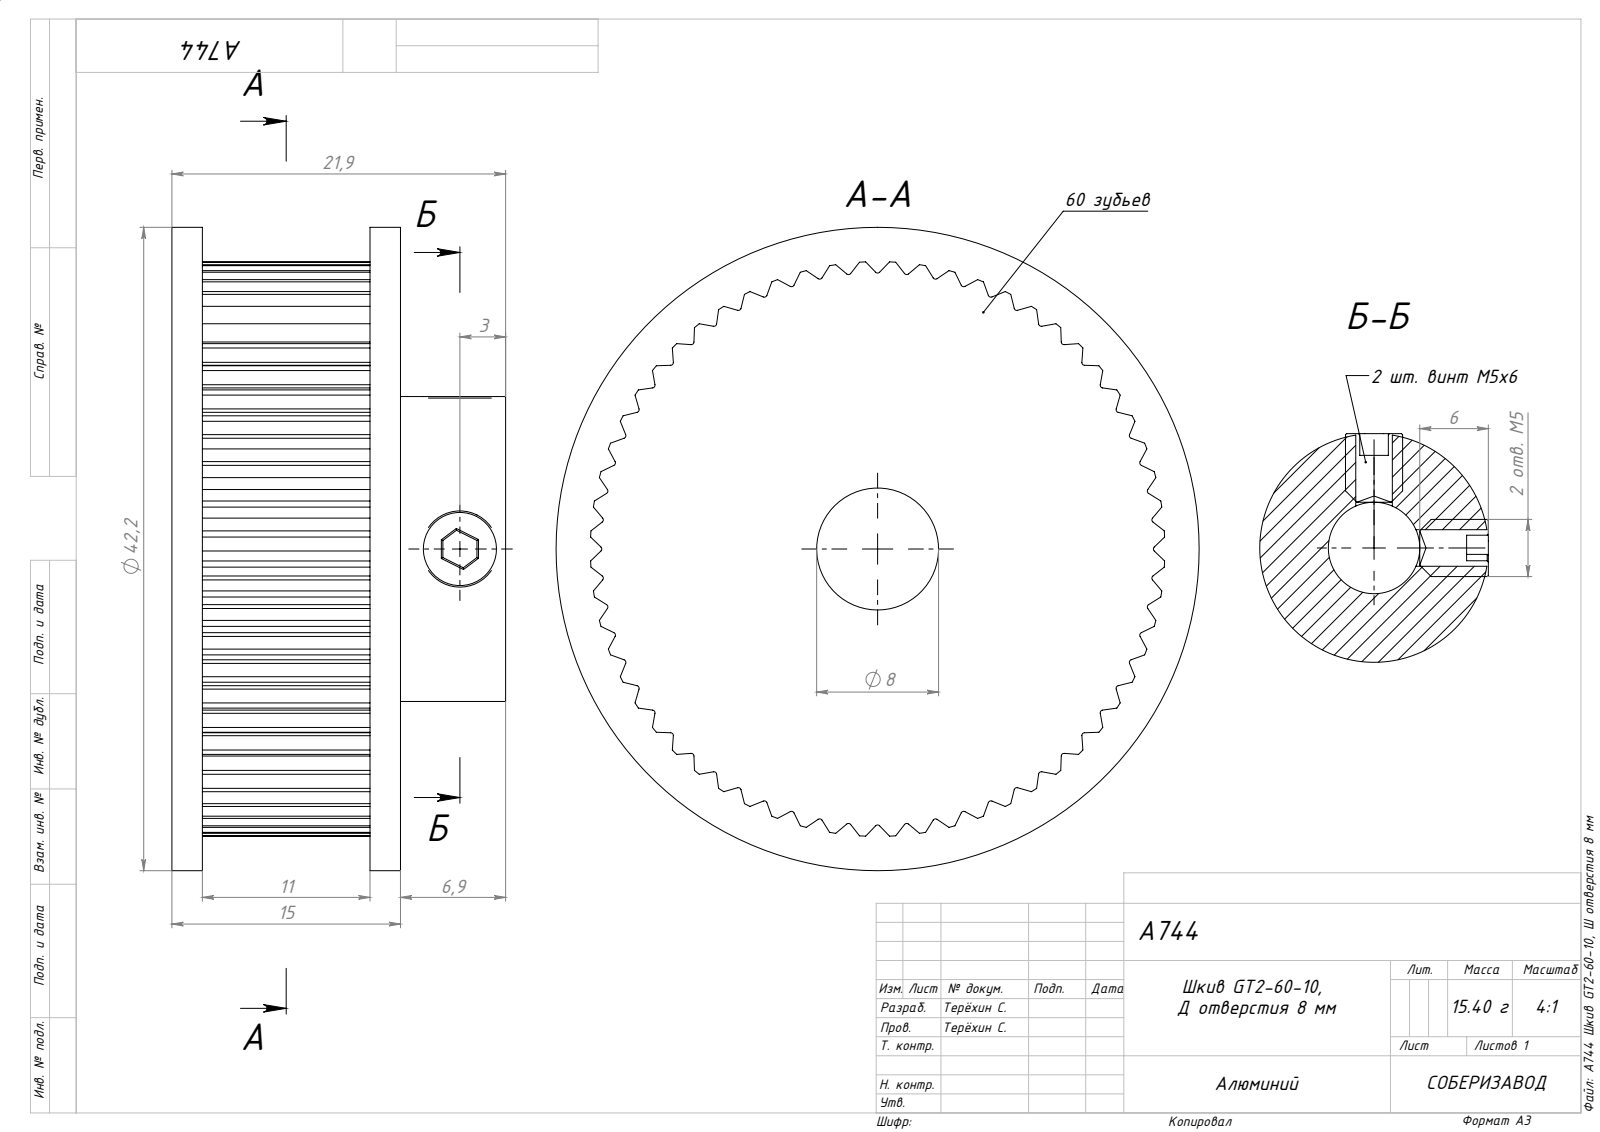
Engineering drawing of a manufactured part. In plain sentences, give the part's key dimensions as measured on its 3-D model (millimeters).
The part is named "A744 Шкив GT2-60-10, Ø отверстия 8 мм; Винт установочный DIN 916 М5х6_M4(4); 39-1(1)". Its 3-D file was written by "SolidWorks 2026 (AUTOMOTIVE_DESIGN)". It is 3 solids with 323 faces: 154 planar, 153 cylindrical and 16 other. Overall it measures 42.2 by 42.2 by 22 millimeters. Its volume is 18 569 cubic millimeters and its surface area 6 820 square millimeters. Round holes: 2 of diameter 3.2, 1 of diameter 8. Round bosses or shafts: 2 of diameter 4, 1 of diameter 42.2, 1 of diameter 32, 1 of diameter 20. Partial cylindrical surfaces (rounded edges, fillets, slot ends): 60 of radius 0.18, 1 of radius 18.85. The main face-to-face distances are 15.1, 2, 13, 15, 13.1, 11, 2.1, 6.9, 19.9, 8.9.
